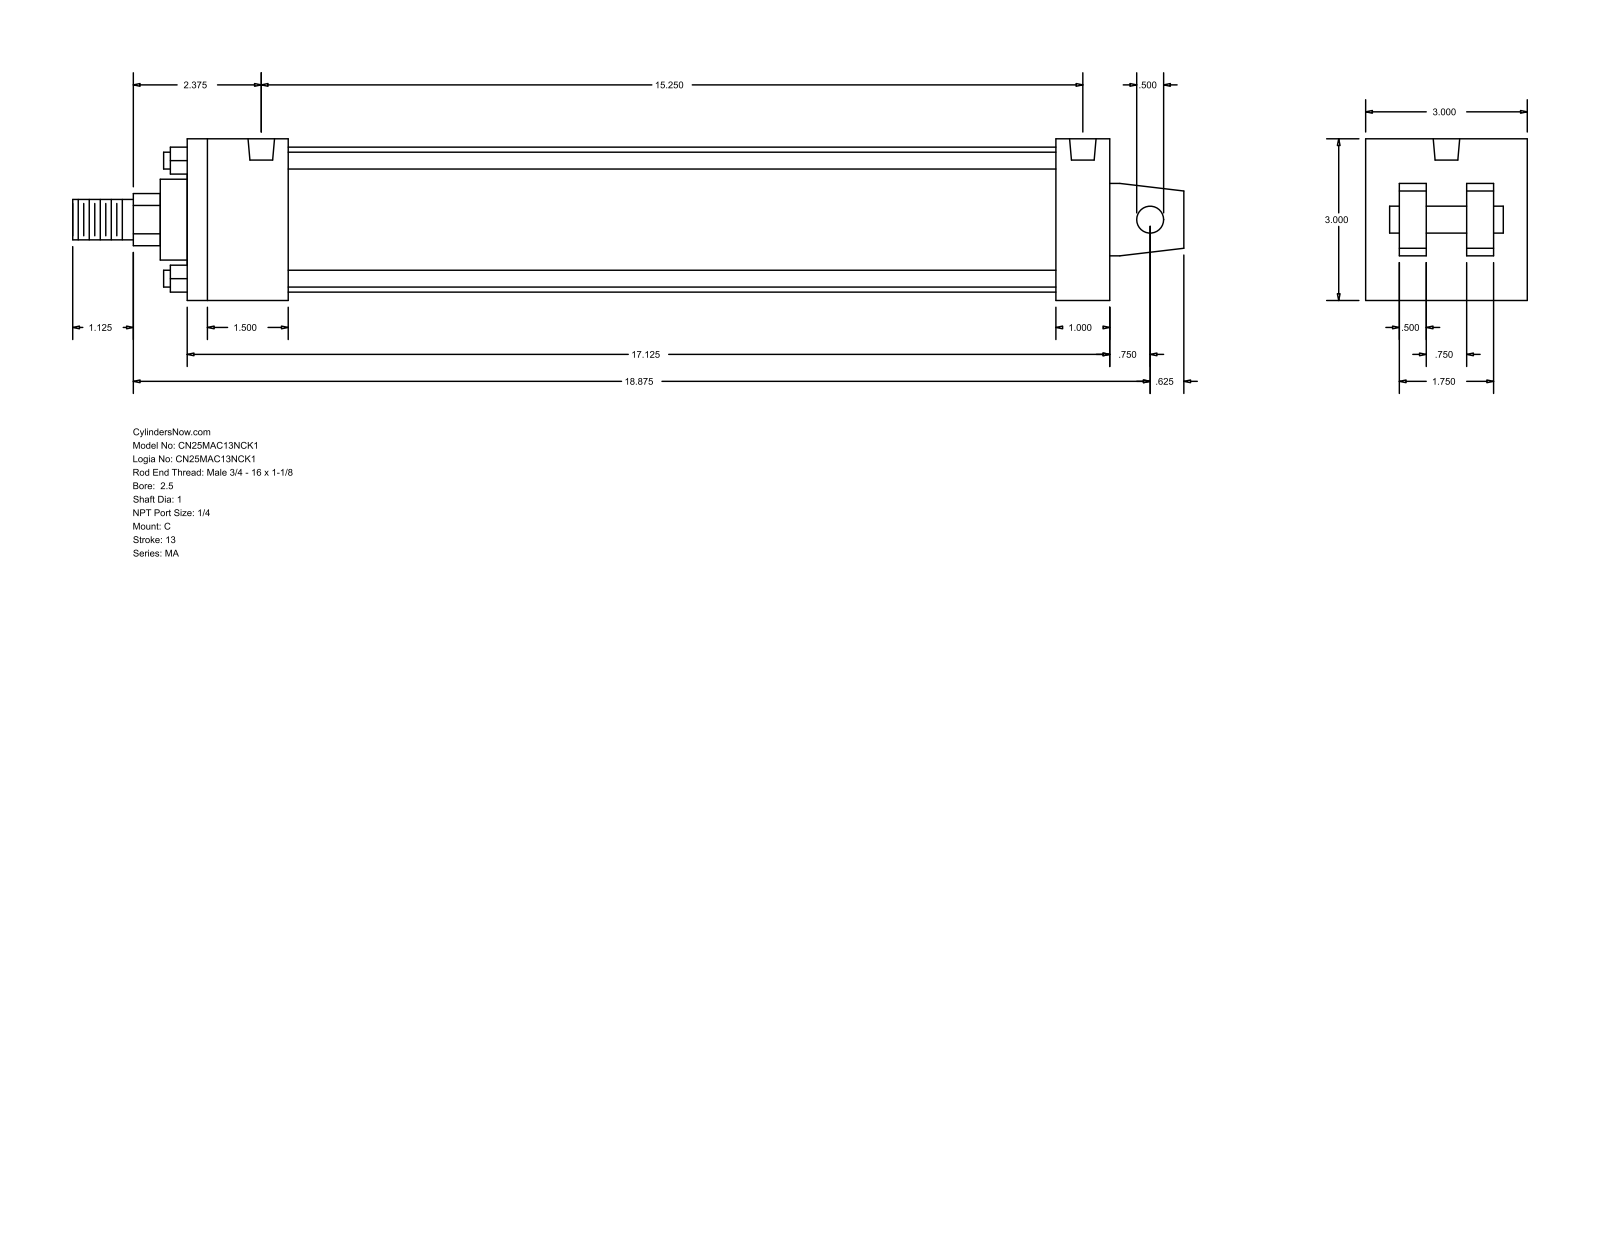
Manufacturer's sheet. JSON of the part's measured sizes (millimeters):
{"part_name": "MA_C__0250_1", "step_written_by": "GSSL Pune (CONFIG_CONTROL_DESIGN)", "units": "millimeters", "bodies": {"solids": 0, "faces": 103, "planar": 76, "cylindrical": 27, "other": 0}, "overall_size": [523.88, 76.2, 76.2], "round_holes": [[7.94, 4], [12.49, 2]], "round_bosses_or_shafts": [[7.94, 4], [68.33, 1], [38.1, 1], [25.4, 1], [19.05, 1], [12.7, 1]], "partial_cylinders_radius": [[12.29, 1]], "face_to_face_distances": [76.2, 434.98, 47.63, 12.7, 60.33, 15.87, 25.4, 28.57, 409.58, 361.95], "hole_center_spacings": [387.35]}
